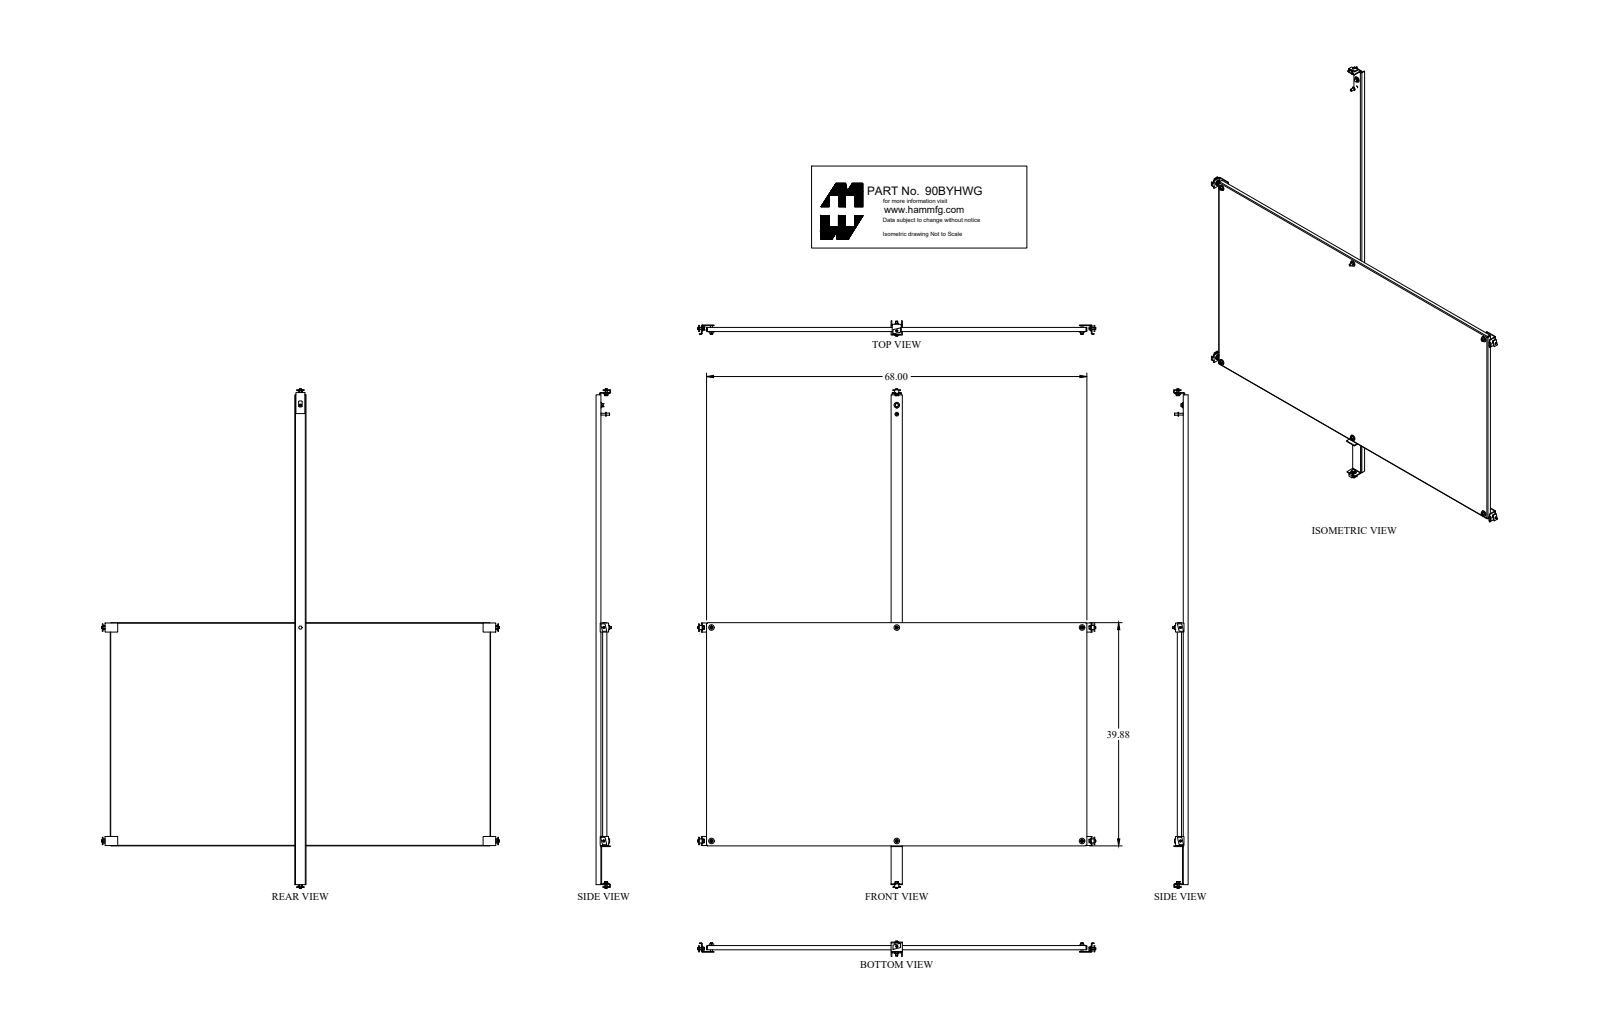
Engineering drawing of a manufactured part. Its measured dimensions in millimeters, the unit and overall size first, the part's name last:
Units: millimetres
Overall size (bounding box): 2258.2 × 1792.8 × 65.9
Round holes (diameter × count): ⌀14.3 ×6, ⌀11.1 ×5, ⌀11.1 ×1, ⌀11.5 ×1
Round bosses / shafts (diameter × count): ⌀16.5 ×6, ⌀8.4 ×6, ⌀9.5 ×4, ⌀9.5 ×2
Partial cylindrical surfaces — rounded edges, fillets, slot ends (radius × count): R1.5 ×11, R4.7 ×11, R1.2 ×4, R3.6 ×4, R5.6 ×2
Main face-to-face distances: 2.4, 3.2, 30.1, 27, 24.6, 27.7, 3.2, 1010.4, 50.8, 47.6
Hole centre spacings: 968.4, 841.4, 841.4, 1282.8, 1282.9, 1682.8, 1941.5, 2149.2
Volume: 5 157 000 mm³ · Surface area: 4 164 000 mm²
Bodies: 14 solids, 305 faces (152 planar, 105 cylindrical, 48 other)
Part name (STEP PRODUCT): 90BYHWG_Default
STEP written by: SolidWorks 2018 (CONFIG_CONTROL_DESIGN)
